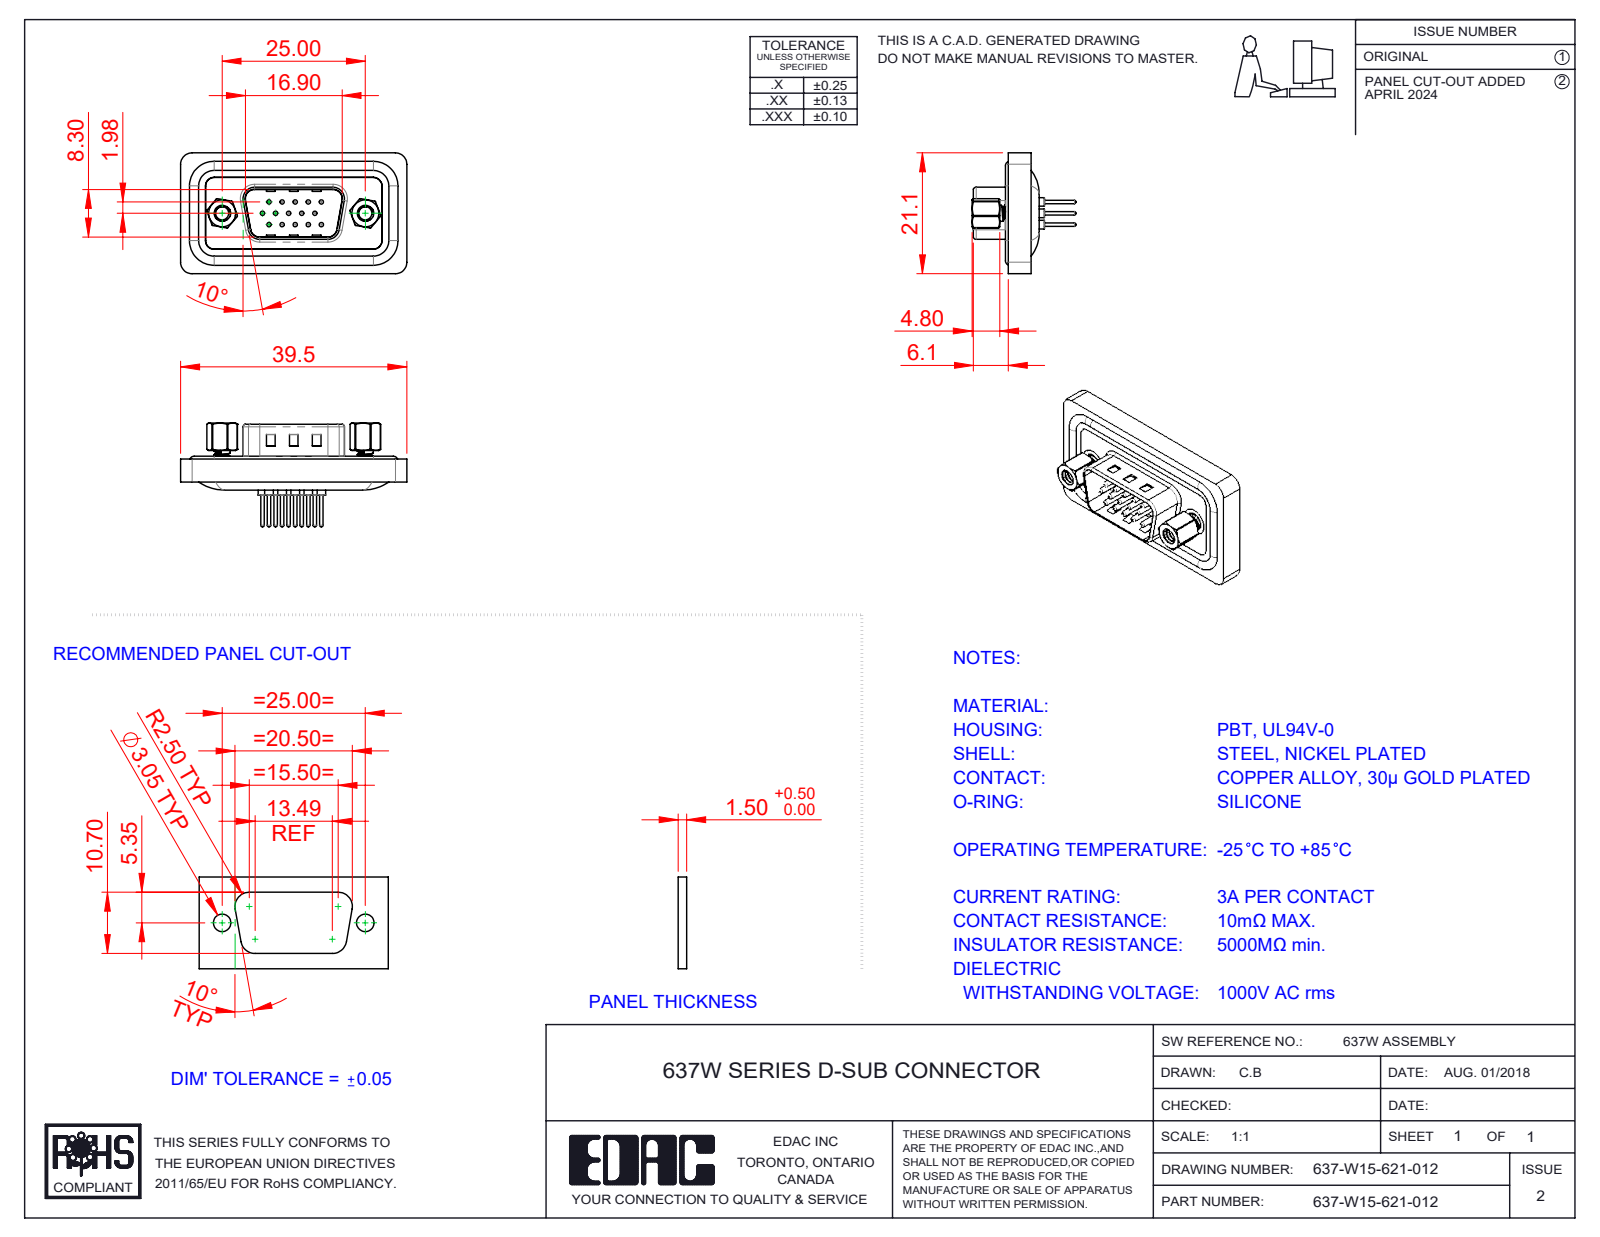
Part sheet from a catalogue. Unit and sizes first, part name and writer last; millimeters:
Units: millimetres
Overall size (bounding box): 39.51 × 21.1 × 17.9
Round holes (diameter × count): ⌀0.75 ×15, ⌀1.5 ×15, ⌀1.6 ×15, ⌀2 ×15, ⌀2.26 ×2, ⌀2.29 ×2, ⌀4 ×2, ⌀4.8 ×2, ⌀5 ×2
Round bosses / shafts (diameter × count): ⌀0.6 ×15, ⌀1.5 ×8, ⌀1.6 ×4, ⌀4.9 ×2, ⌀2.79 ×2, ⌀5 ×1
Partial cylindrical surfaces — rounded edges, fillets, slot ends (radius × count): R1.5 ×14, R2 ×14, R0.5 ×8, R2.7 ×6, R0.9 ×4, R1.6 ×4, R4.3 ×4, R0.4 ×2
Main face-to-face distances: 0.4, 1.1, 2.9, 1.6, 2.5, 0.5, 4, 3.6, 1.8, 0.7
Hole centre spacings: 3.96, 2.28, 4.57, 2.29, 6.05, 6.04, 7.92, 6.86
Volume: 4 003 mm³ · Surface area: 6 826 mm²
Bodies: 23 solids, 1031 faces (246 planar, 448 cylindrical, 337 other)
Part name (STEP PRODUCT): 637-W15-621-012; 637W Contact Row 3_21; 637W Contact Row 2_21; 637W 4-40 Hex Standoff (+5 more)
STEP written by: SolidWorks 2016 (CONFIG_CONTROL_DESIGN)
